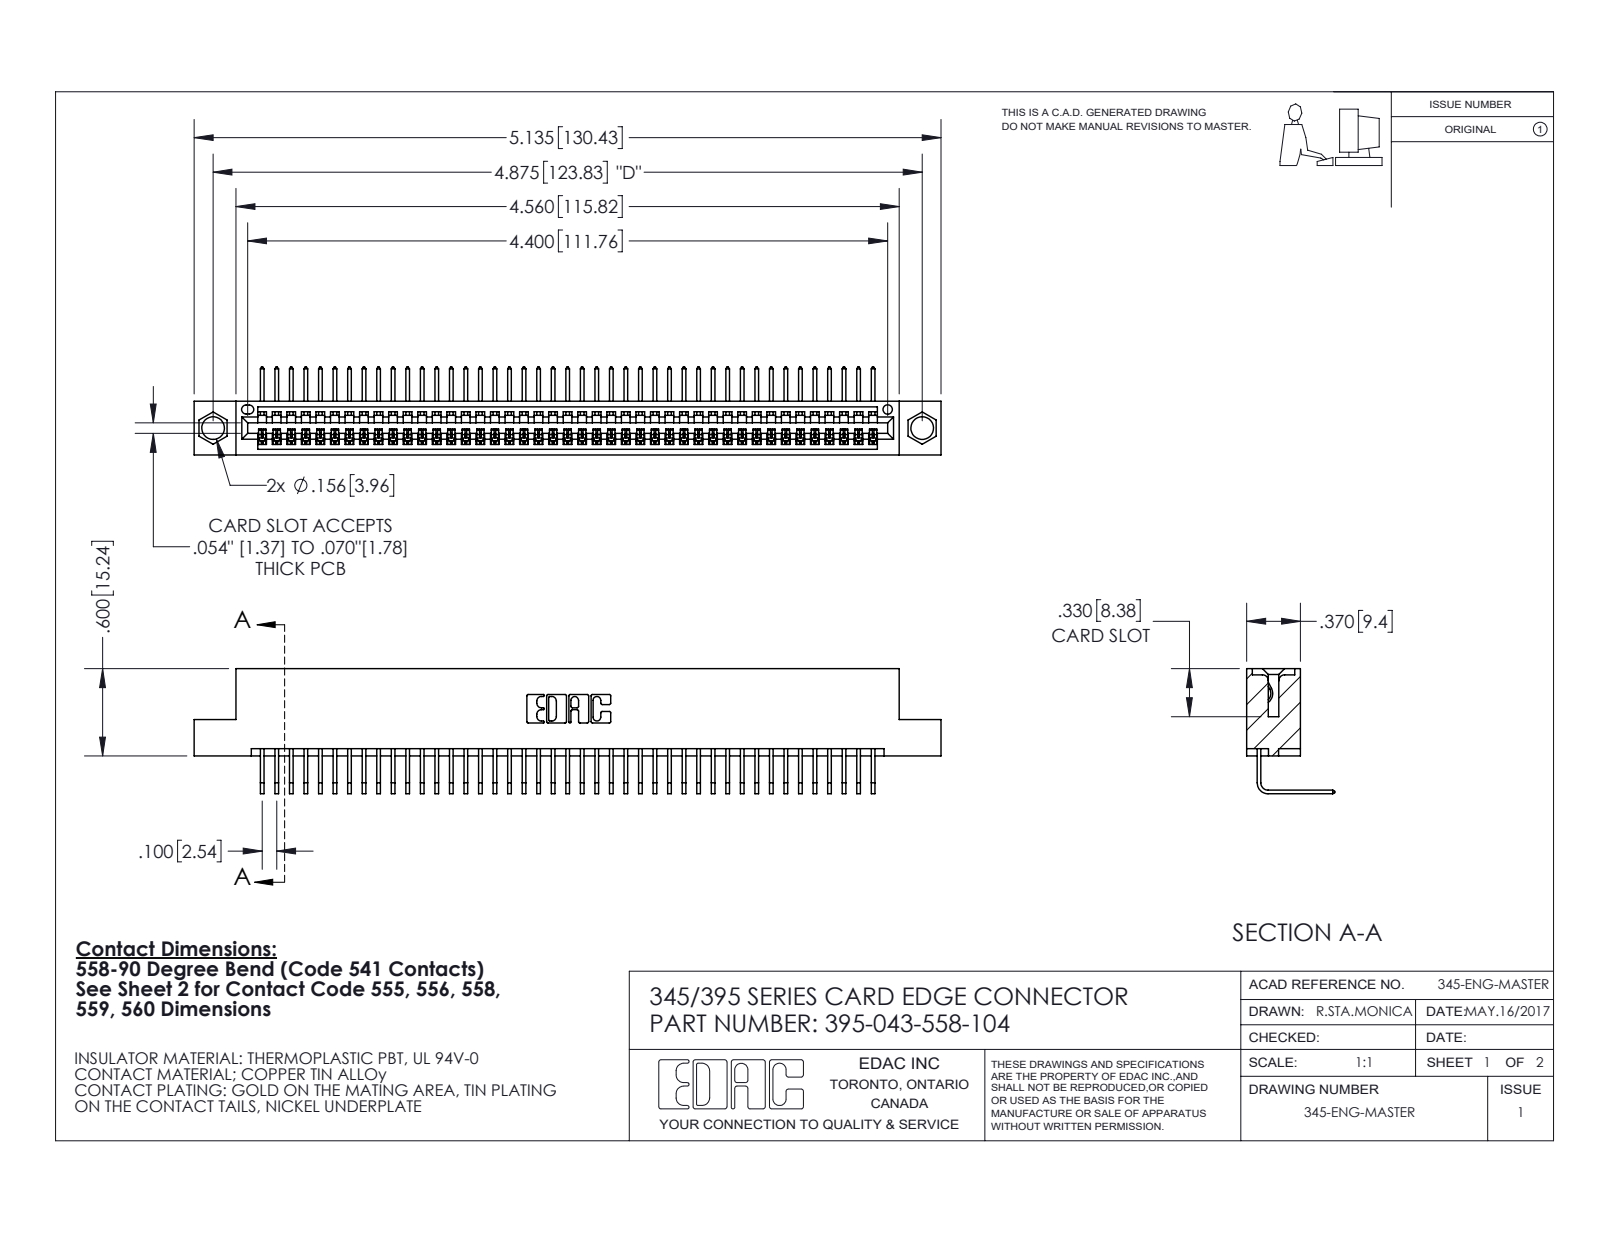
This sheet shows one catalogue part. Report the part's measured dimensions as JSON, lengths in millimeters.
{"part_name": "345 Part_Flush Mounting Lugs - 0.156 Dia-TI; 345-292-001_558 Tail - 2; 395-043-558-104", "step_written_by": "SolidWorks 2020 (CONFIG_CONTROL_DESIGN)", "units": "millimeters", "bodies": {"solids": 44, "faces": 2720, "planar": 1900, "cylindrical": 820, "other": 0}, "overall_size": [130.4, 21.8, 15.4], "volume_mm3": 12400, "surface_area_mm2": 17220, "round_holes": [[4, 2], [1.6, 1]], "partial_cylinders_radius": [[0.2, 86], [0.3, 22], [0.2, 6], [0.8, 6], [0.7, 3], [0.8, 2], [1, 2], [0.4, 1]], "face_to_face_distances": [1.8, 7.6, 9.4, 5.1, 2.5, 6.9, 0.6, 5.7, 3.8, 1.8], "hole_center_spacings": [6.9, 117.8, 123.8]}
